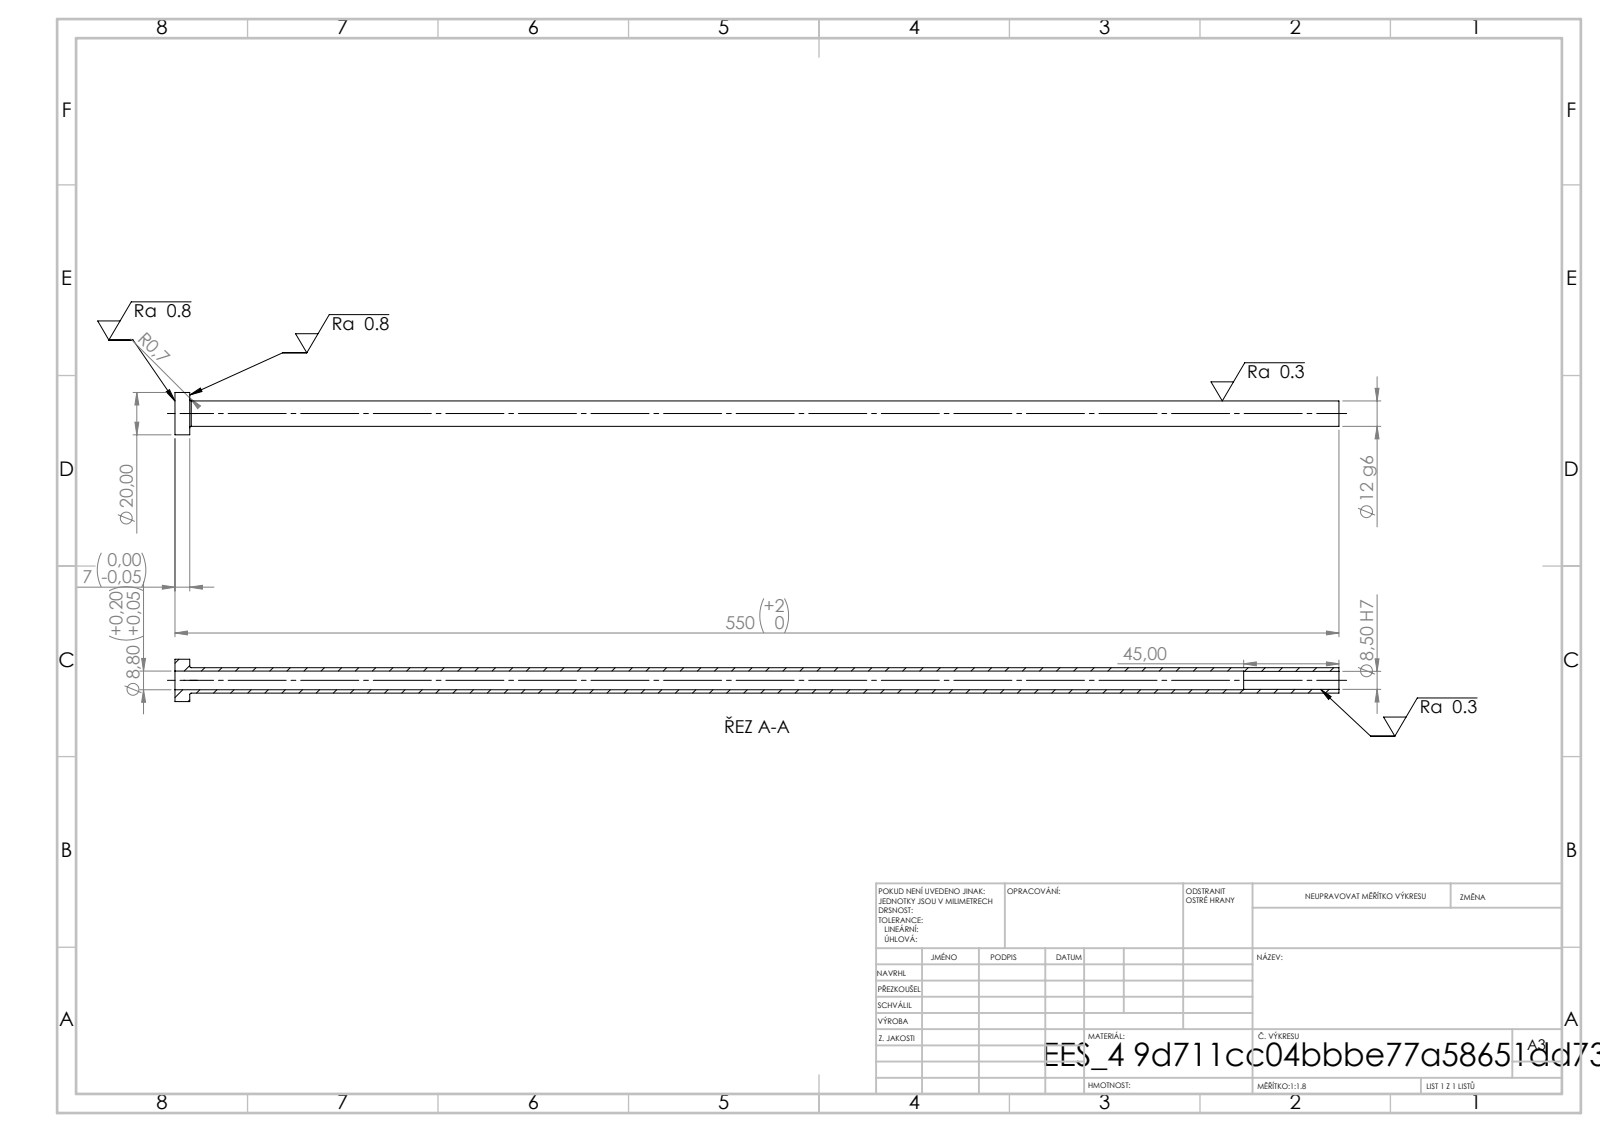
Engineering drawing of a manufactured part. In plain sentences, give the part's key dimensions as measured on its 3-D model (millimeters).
Its 3-D file was written by "SolidWorks 2019 (CONFIG_CONTROL_DESIGN)". It is 1 solid with 14 faces: 4 planar, 8 cylindrical and 2 other. Overall it measures 550 by 20 by 20 millimeters. Its volume is 30 347 cubic millimeters and its surface area 36 577 square millimeters. Round holes: 1 of diameter 8.5, 1 of diameter 8.8. Round bosses or shafts: 1 of diameter 20, 1 of diameter 12. The main face-to-face distances are 7, 550, 543, 505, 498, 45.
